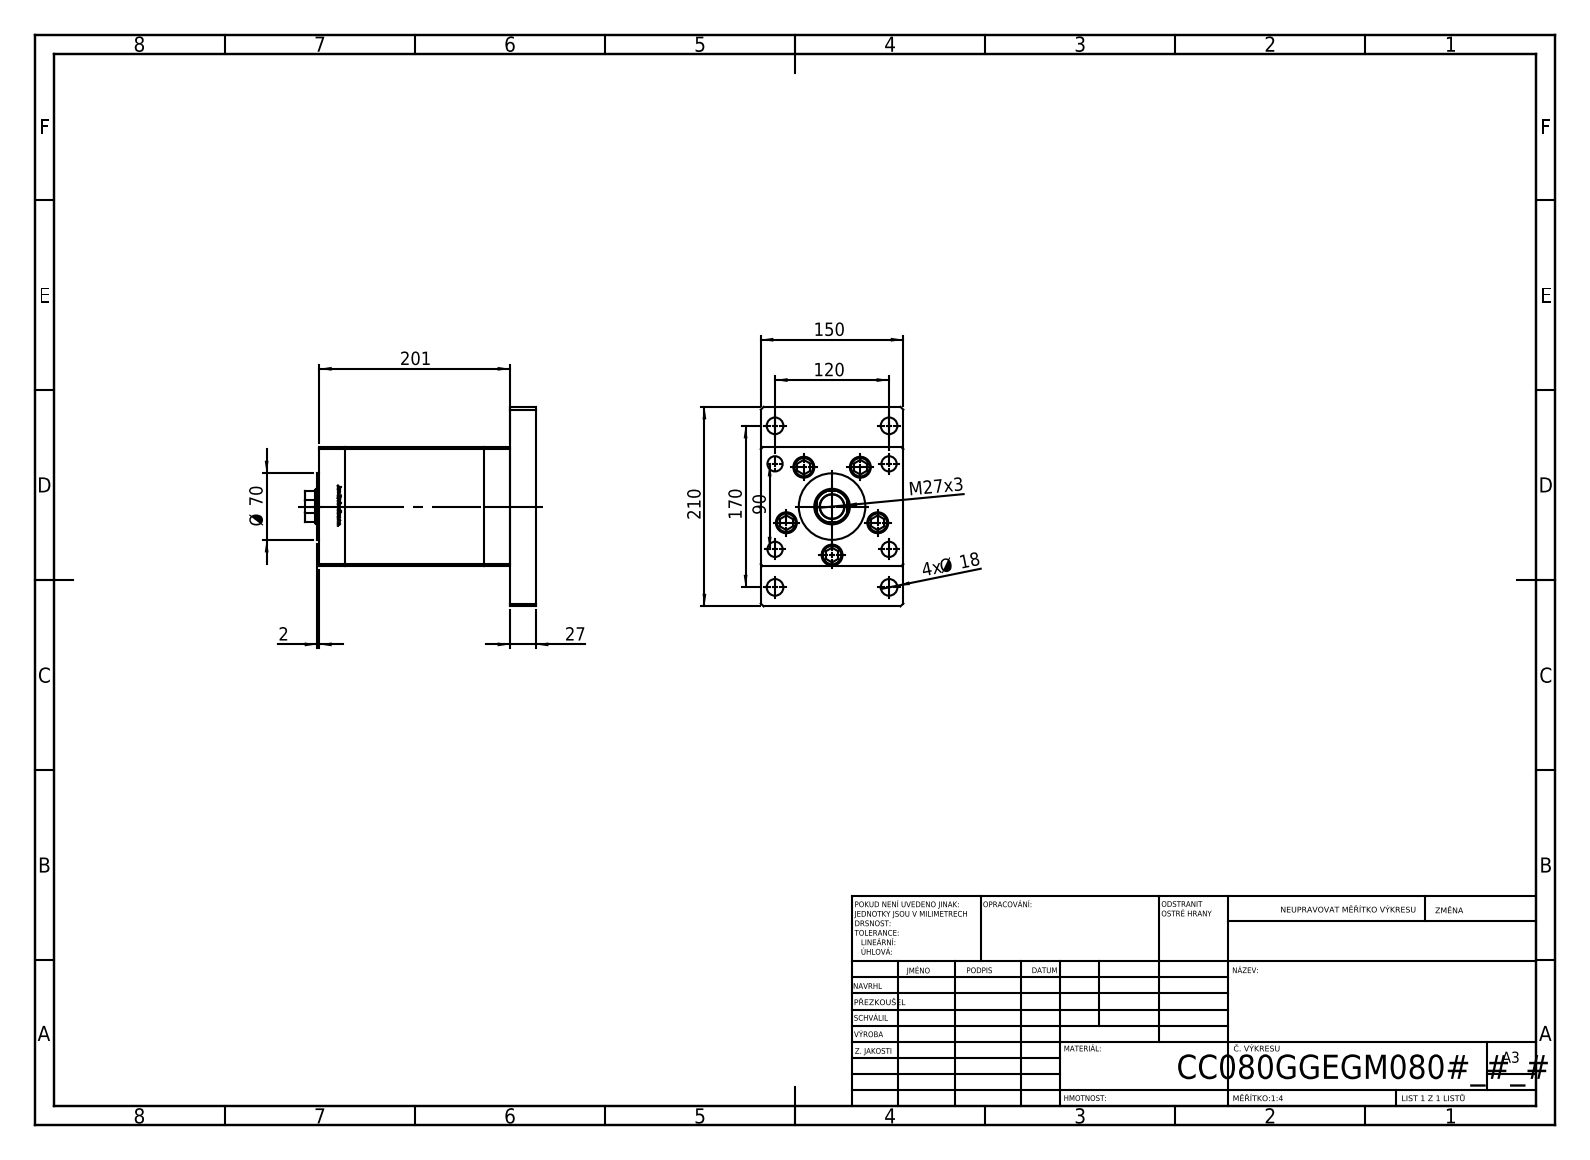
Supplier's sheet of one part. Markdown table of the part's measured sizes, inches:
| quantity | value |
| --- | --- |
| part name | ALLEN BOLT; V220C_FRONT_G; V220C_VC_G; V220C_F (+2 more) |
| STEP written by | SolidWorks 2019 (CONFIG_CONTROL_DESIGN) |
| units | inches |
| bodies | 19 solids, 1313 faces (518 planar, 189 cylindrical, 606 other) |
| overall size | 9.567 × 8.268 × 5.906 |
| volume | 246.8 in³ |
| surface area | 696.3 in² |
| round holes (diameter × count) | 0.63 × 9, 0.689 × 9, 0.866 × 5, 0.827 × 4, 0.079 × 2, 0.518 × 2, 1.004 × 1, 1.417 × 1, 1.476 × 1, 4.016 × 1 |
| round bosses / shafts (diameter × count) | 0.315 × 9, 0.827 × 5, 3.15 × 1, 2.756 × 1 |
| partial cylindrical surfaces (radius × count) | 0.037 × 2, 0.689 × 1 |
| main face-to-face distances | 1.063, 6.85, 7.913, 5.906, 5.787, 4.921, 2.126, 6.594, 0.079, 8.976 |
| hole center spacings | 2.008, 1.575, 2.953, 4.096, 4.724, 4.98, 5.118, 6.965 |
